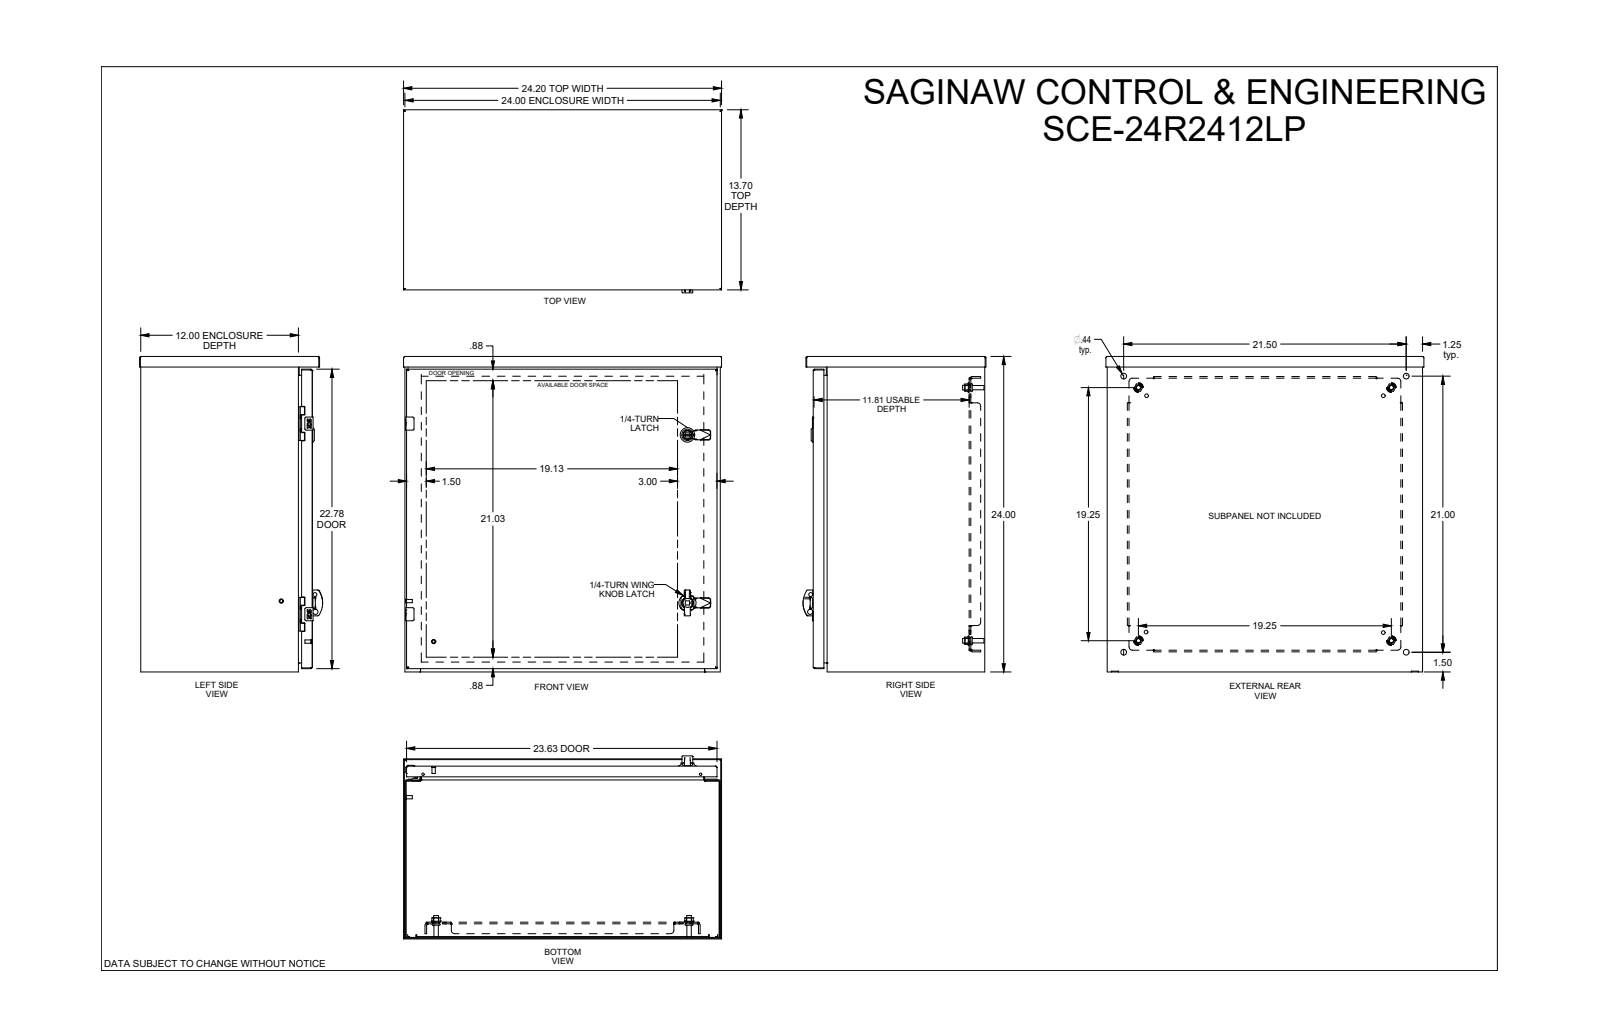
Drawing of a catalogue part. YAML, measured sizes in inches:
part_name: "SCE-24R2412LP"
step_written_by: "SolidWorks 2019 (CONFIG_CONTROL_DESIGN)"
units: inches
bodies: {solids: 0, faces: 2429, planar: 1160, cylindrical: 823, other: 446}
overall_size: [24.2, 24, 13.927]
round_holes:
  - {diameter: 0.172, count: 4}
  - {diameter: 0.205, count: 4}
  - {diameter: 0.244, count: 4}
  - {diameter: 0.266, count: 4}
  - {diameter: 0.281, count: 4}
  - {diameter: 0.367, count: 4}
  - {diameter: 0.375, count: 4}
  - {diameter: 0.438, count: 4}
  - {diameter: 0.5, count: 4}
  - {diameter: 0.04, count: 2}
  - {diameter: 0.156, count: 2}
  - {diameter: 0.218, count: 2}
round_bosses_or_shafts:
  - {diameter: 0.17, count: 6}
  - {diameter: 0.366, count: 4}
  - {diameter: 0.332, count: 4}
  - {diameter: 0.25, count: 4}
  - {diameter: 0.24, count: 4}
  - {diameter: 0.196, count: 3}
  - {diameter: 0.866, count: 2}
  - {diameter: 0.802, count: 2}
partial_cylinders:
  - {radius: 0.015, count: 72}
  - {radius: 0.012, count: 60}
  - {radius: 0.01, count: 26}
  - {radius: 0.02, count: 24}
  - {radius: 0.112, count: 23}
  - {radius: 0.06, count: 22}
  - {radius: 0.052, count: 19}
  - {radius: 0.03, count: 15}
face_to_face_distances: [0.06, 23.94, 0.06, 12.933, 12.993, 24, 23.88, 13.053, 12.993, 0.125]
hole_center_spacings: [14.5, 0.024, 0.493, 0.985, 18.641, 20.394, 28.638, 0.875]
